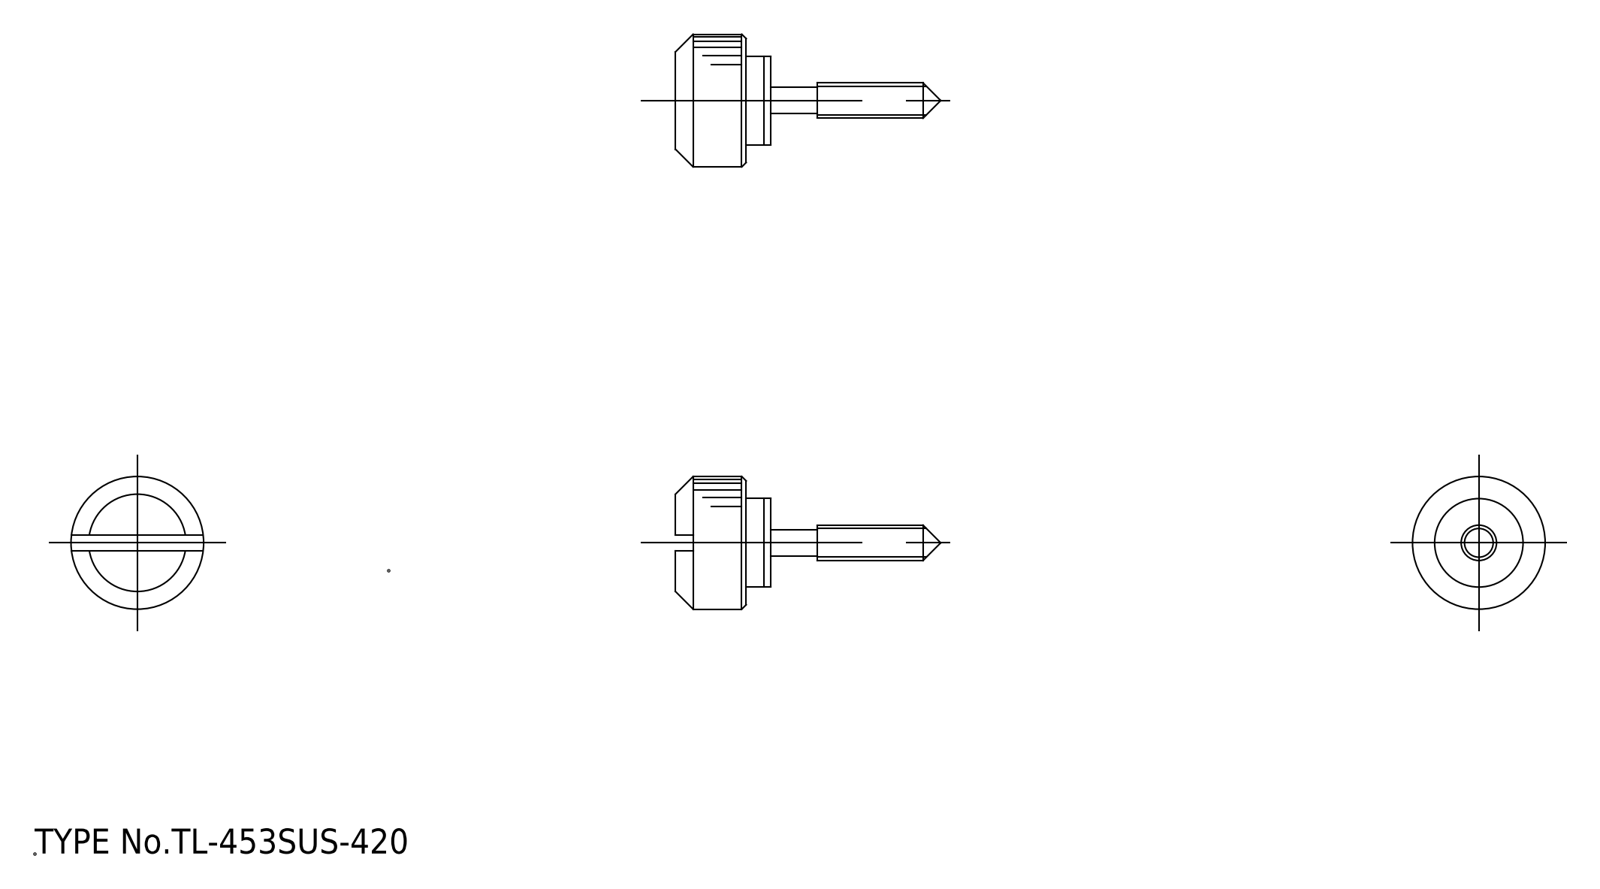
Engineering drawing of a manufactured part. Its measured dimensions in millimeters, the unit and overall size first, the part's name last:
Units: millimetres
Overall size (bounding box): 30 × 15 × 15
Round bosses / shafts (diameter × count): ⌀15 ×1, ⌀10 ×1, ⌀4 ×1, ⌀3 ×1
Partial cylindrical surfaces — rounded edges, fillets, slot ends (radius × count): R0.8 ×3, R1.55 ×1
Main face-to-face distances: 8, 2, 10, 10.8, 2.8, 0.8, 6, 8.8, 1.8, 16
Volume: 1 686 mm³ · Surface area: 1 159 mm²
Bodies: 2 solids, 38 faces (16 planar, 16 cylindrical, 6 other)
Part name (STEP PRODUCT): washer; knob
STEP written by: spGate 19.8.4 (****-****-****-****) (AUTOMOTIVE_DESIGN)
